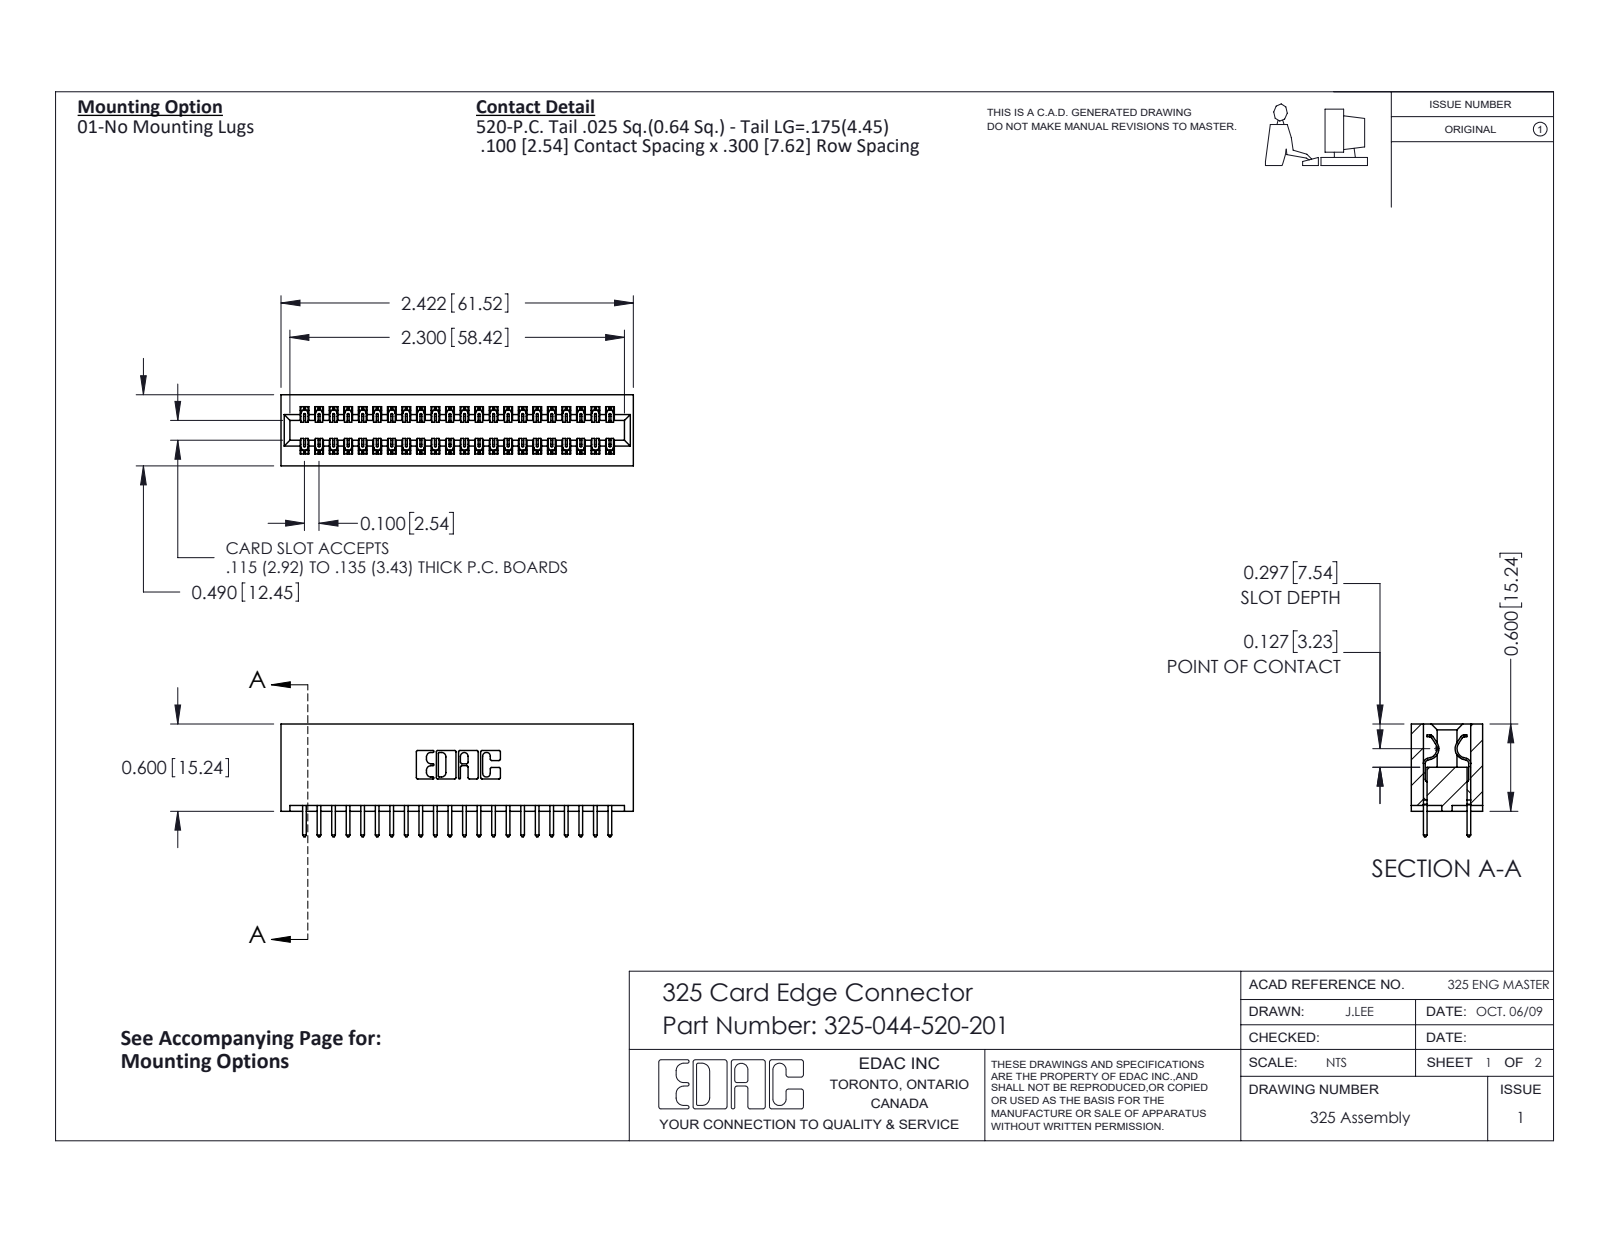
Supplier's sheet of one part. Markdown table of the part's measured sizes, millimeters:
| quantity | value |
| --- | --- |
| part name | 325 Part_Lugless; 325-292-001_325-293-120; 325-044-520-201 |
| STEP written by | SolidWorks 2016 (CONFIG_CONTROL_DESIGN) |
| units | millimeters |
| bodies | 45 solids, 2394 faces (1650 planar, 744 cylindrical, 0 other) |
| overall size | 61.5 × 19.7 × 12.4 |
| volume | 8 360 mm³ |
| surface area | 10 220 mm² |
| partial cylindrical surfaces (radius × count) | 0.2 × 66, 0.3 × 44, 0.3 × 22, 0.2 × 6, 0.8 × 6, 0.7 × 3, 0.4 × 2, 0.6 × 2 |
| main face-to-face distances | 2.1, 10.3, 7.6, 12.4, 2.7, 9.7, 0.6, 8.3, 2.5, 14.2 |
